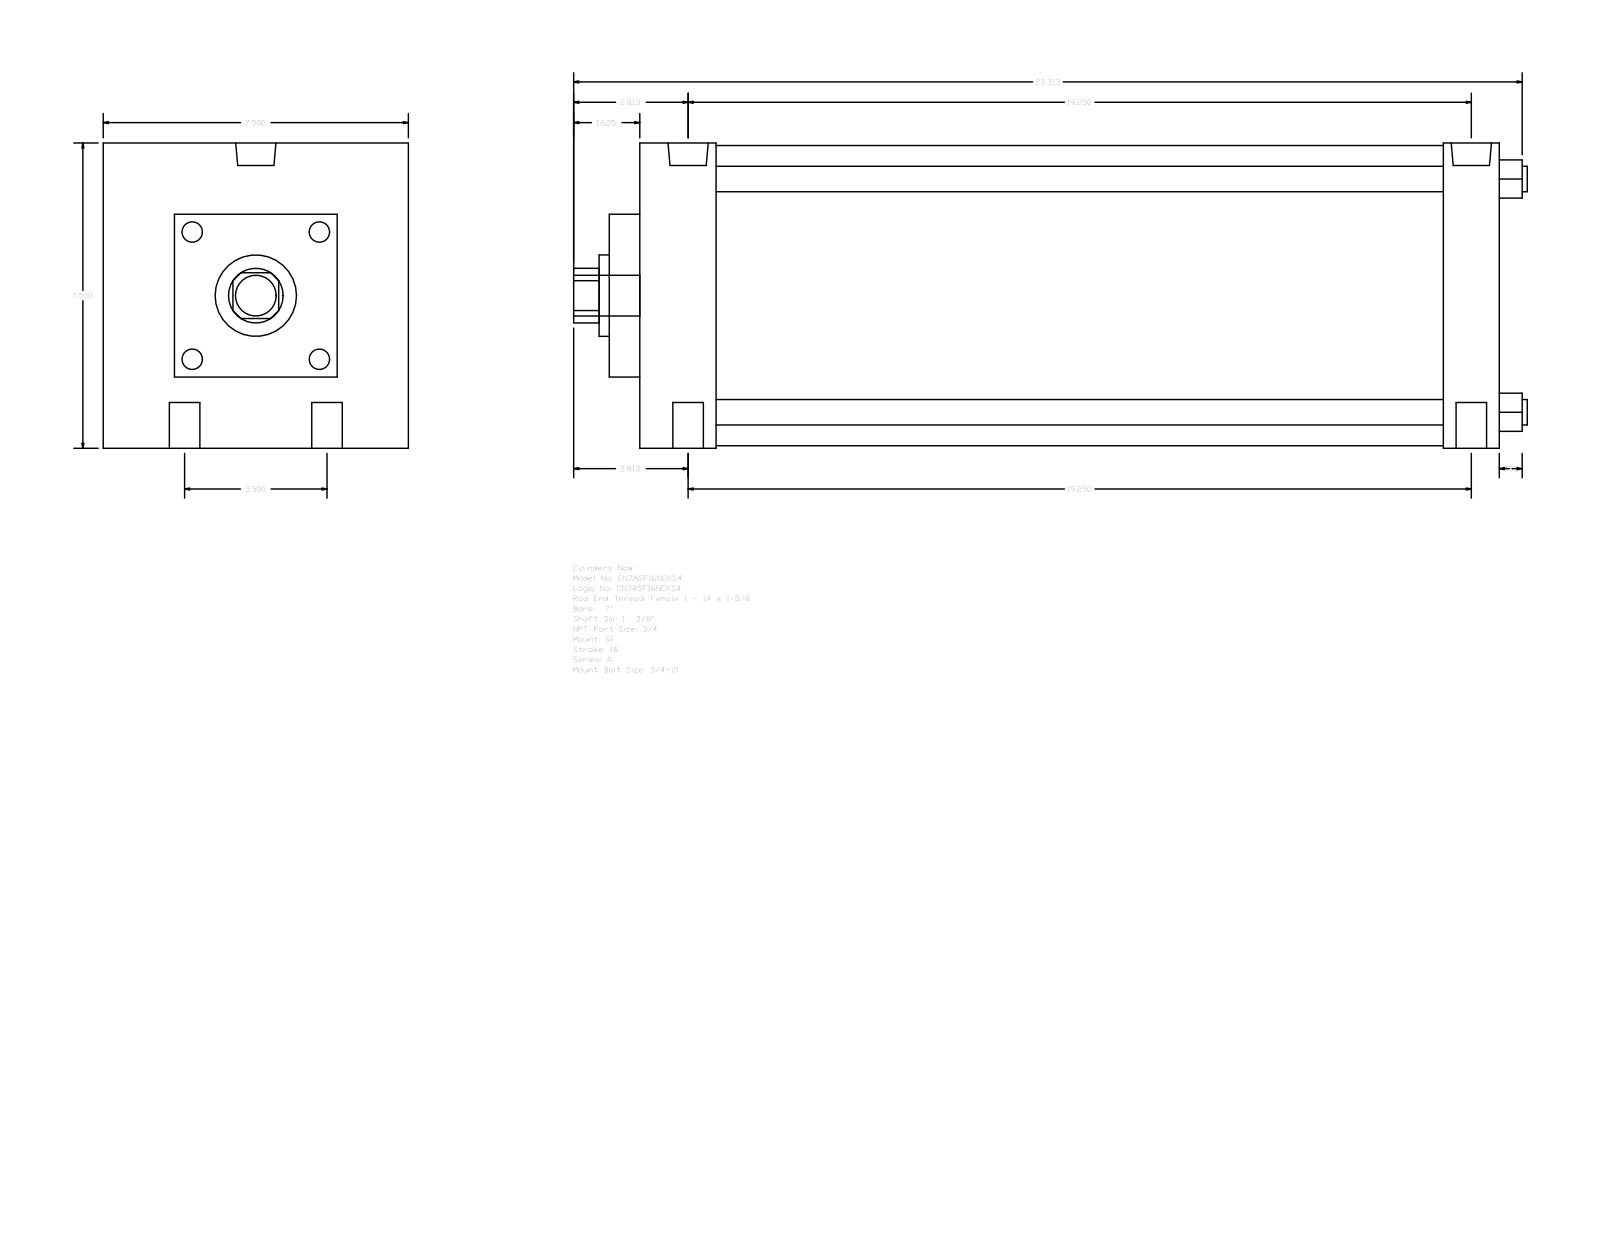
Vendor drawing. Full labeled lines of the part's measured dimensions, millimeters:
Part name (STEP PRODUCT): A_SF__0700_1.375
STEP written by: GSSL Pune (CONFIG_CONTROL_DESIGN)
Units: millimetres
Bodies: 0 solids, 93 faces (67 planar, 26 cylindrical, 0 other)
Overall size (bounding box): 595.31 × 190.5 × 190.5
Round holes (diameter × count): ⌀19.05 ×4, ⌀15.08 ×2, ⌀25.12 ×2, ⌀34.92 ×1, ⌀50.8 ×1
Round bosses / shafts (diameter × count): ⌀15.88 ×4, ⌀187.32 ×1, ⌀25.4 ×1
Partial cylindrical surfaces — rounded edges, fillets, slot ends (radius × count): R17.06 ×1
Main face-to-face distances: 190.5, 536.58, 19.04, 555.62, 66.67, 520.69, 47.63, 501.65, 454.02, 488.95
Hole centre spacings: 44.45, 490.97, 488.95, 88.9, 496.97, 477.83
